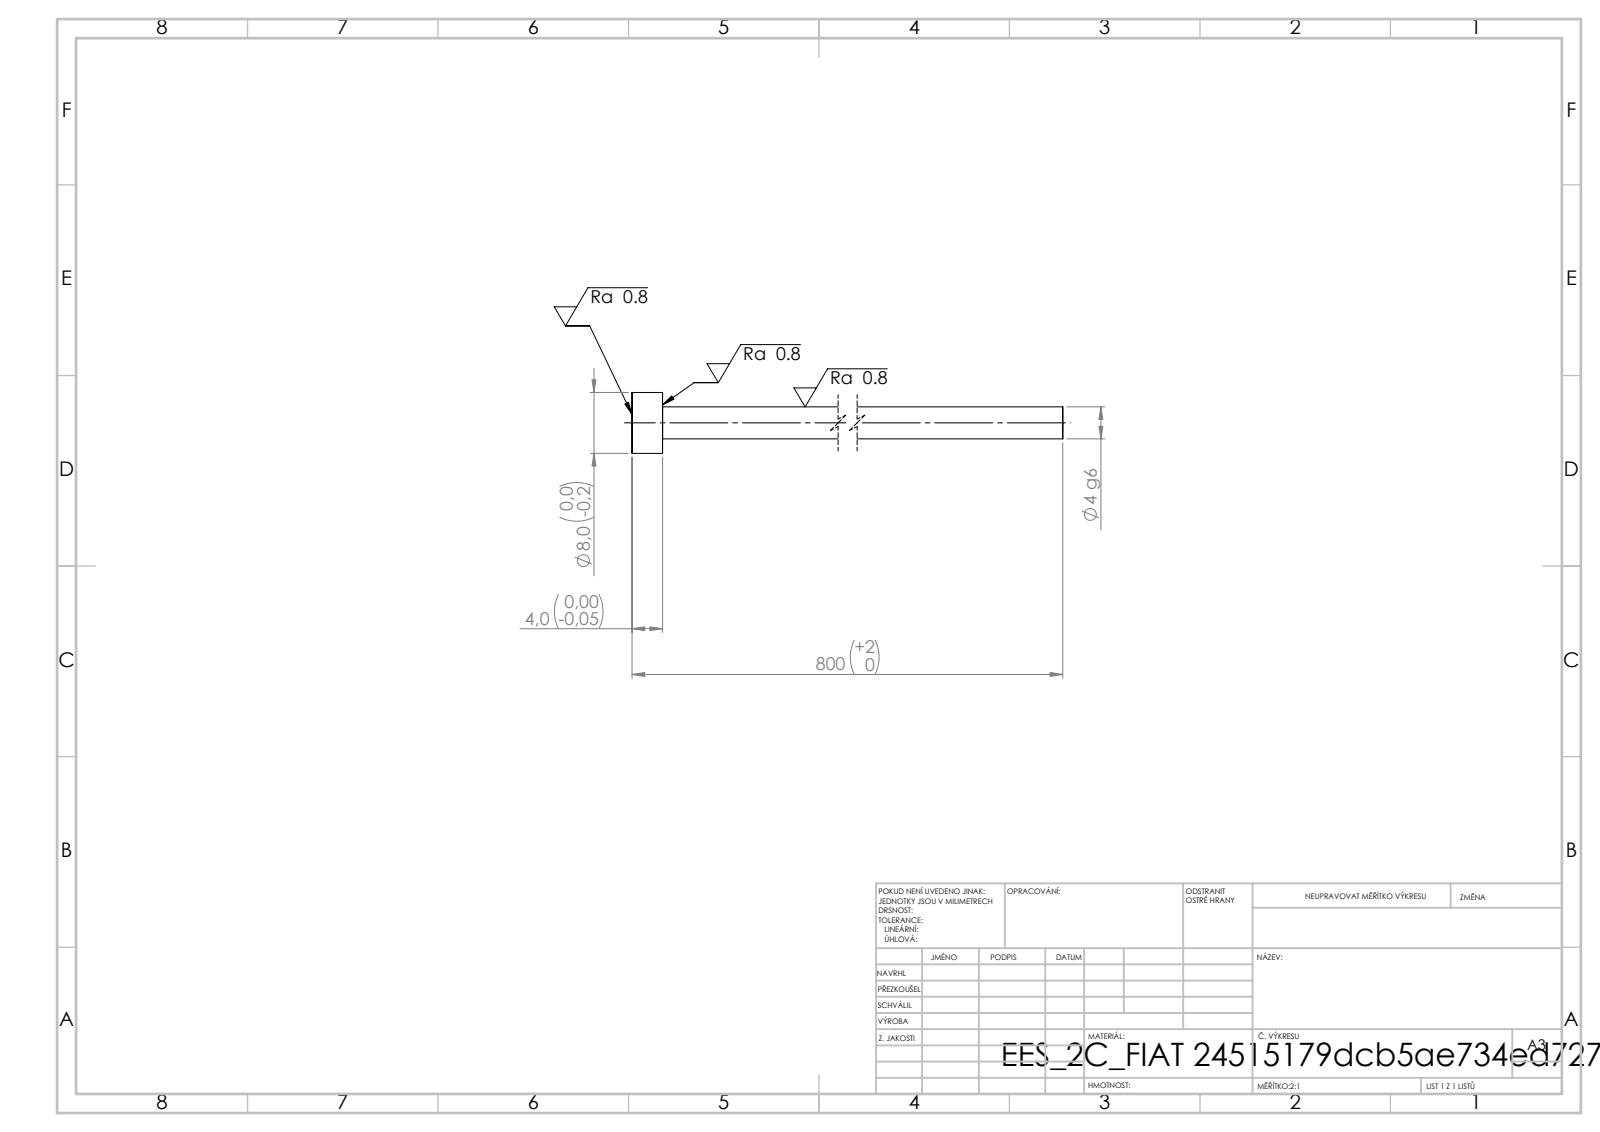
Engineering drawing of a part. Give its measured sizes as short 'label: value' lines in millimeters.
written by: SolidWorks 2019 (CONFIG_CONTROL_DESIGN)
unit: mm
bodies: 1 solid, 7 faces (3 planar, 4 cylindrical, 0 other)
size: 800 × 8 × 8
volume: 11 229 mm³; area: 10 704 mm²
bosses: 1× ⌀8, 1× ⌀4.2
face distances: 4, 800, 796
